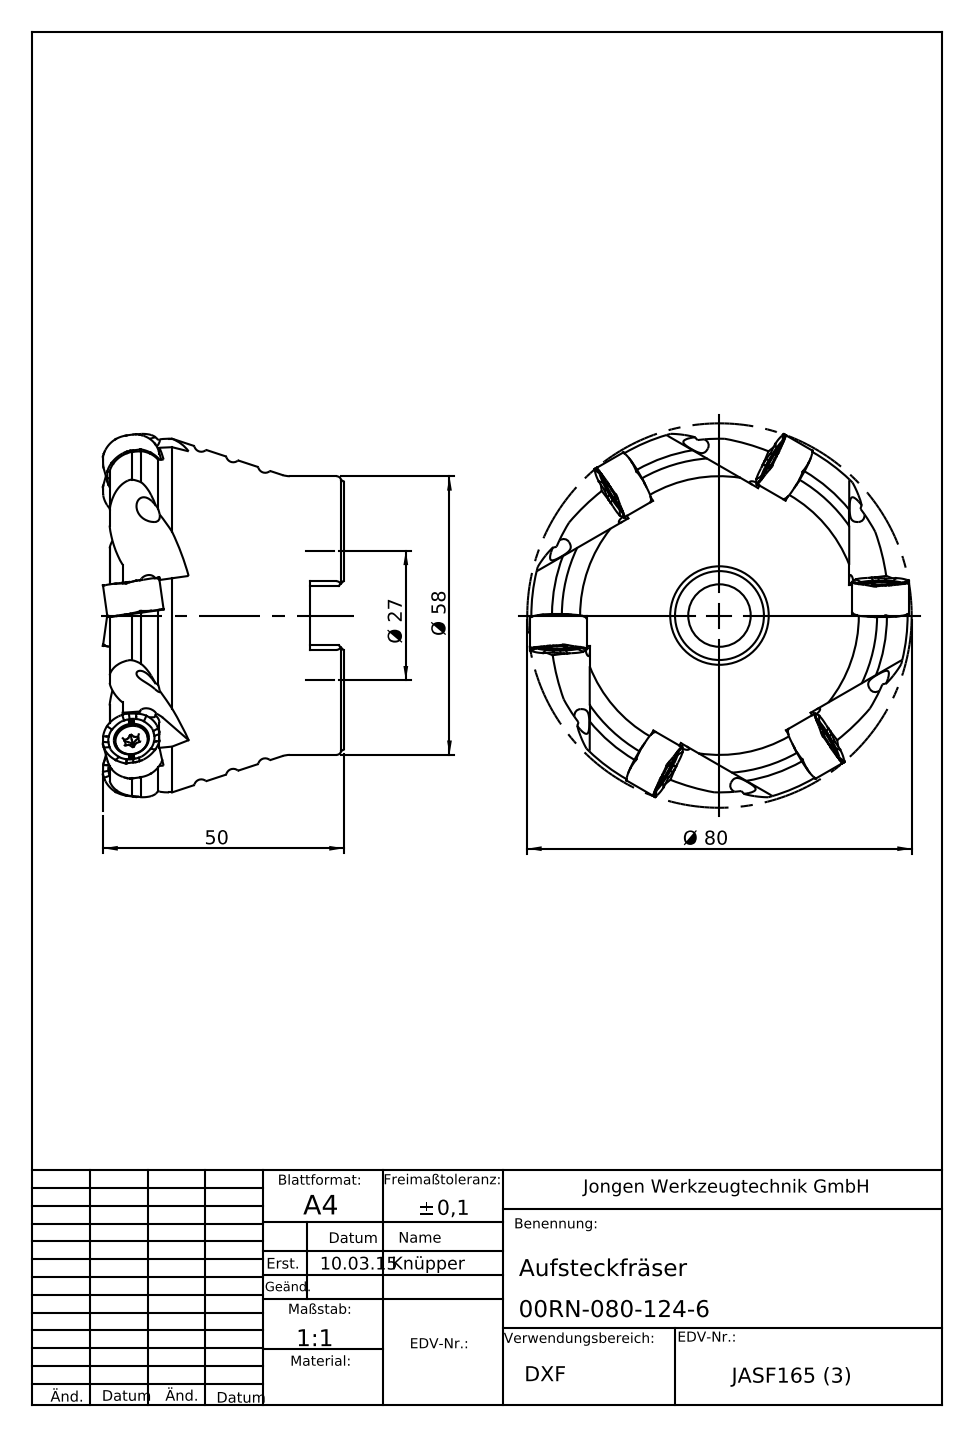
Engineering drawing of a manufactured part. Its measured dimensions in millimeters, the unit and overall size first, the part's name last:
Units: millimetres
Overall size (bounding box): 79.97 × 79.97 × 49.98
Round holes (diameter × count): ⌀3 ×6, ⌀13 ×1, ⌀18.5 ×1, ⌀27 ×1, ⌀27.15 ×1, ⌀27.3 ×1
Round bosses / shafts (diameter × count): ⌀58 ×1
Partial cylindrical surfaces — rounded edges, fillets, slot ends (radius × count): R2.15 ×6, R2.5 ×6, R4.5 ×6, R6 ×6, R36.8 ×1
Main face-to-face distances: 46, 7.05, 38.95, 25, 17.95, 21, 12.4, 32, 24.95, 7
Volume: 142 723 mm³ · Surface area: 24 842 mm²
Bodies: 1 solid, 197 faces (77 planar, 57 cylindrical, 63 other)
Part name (STEP PRODUCT): 00RN_080_124_6
STEP written by: SolidWorks 2016 (AUTOMOTIVE_DESIGN)
